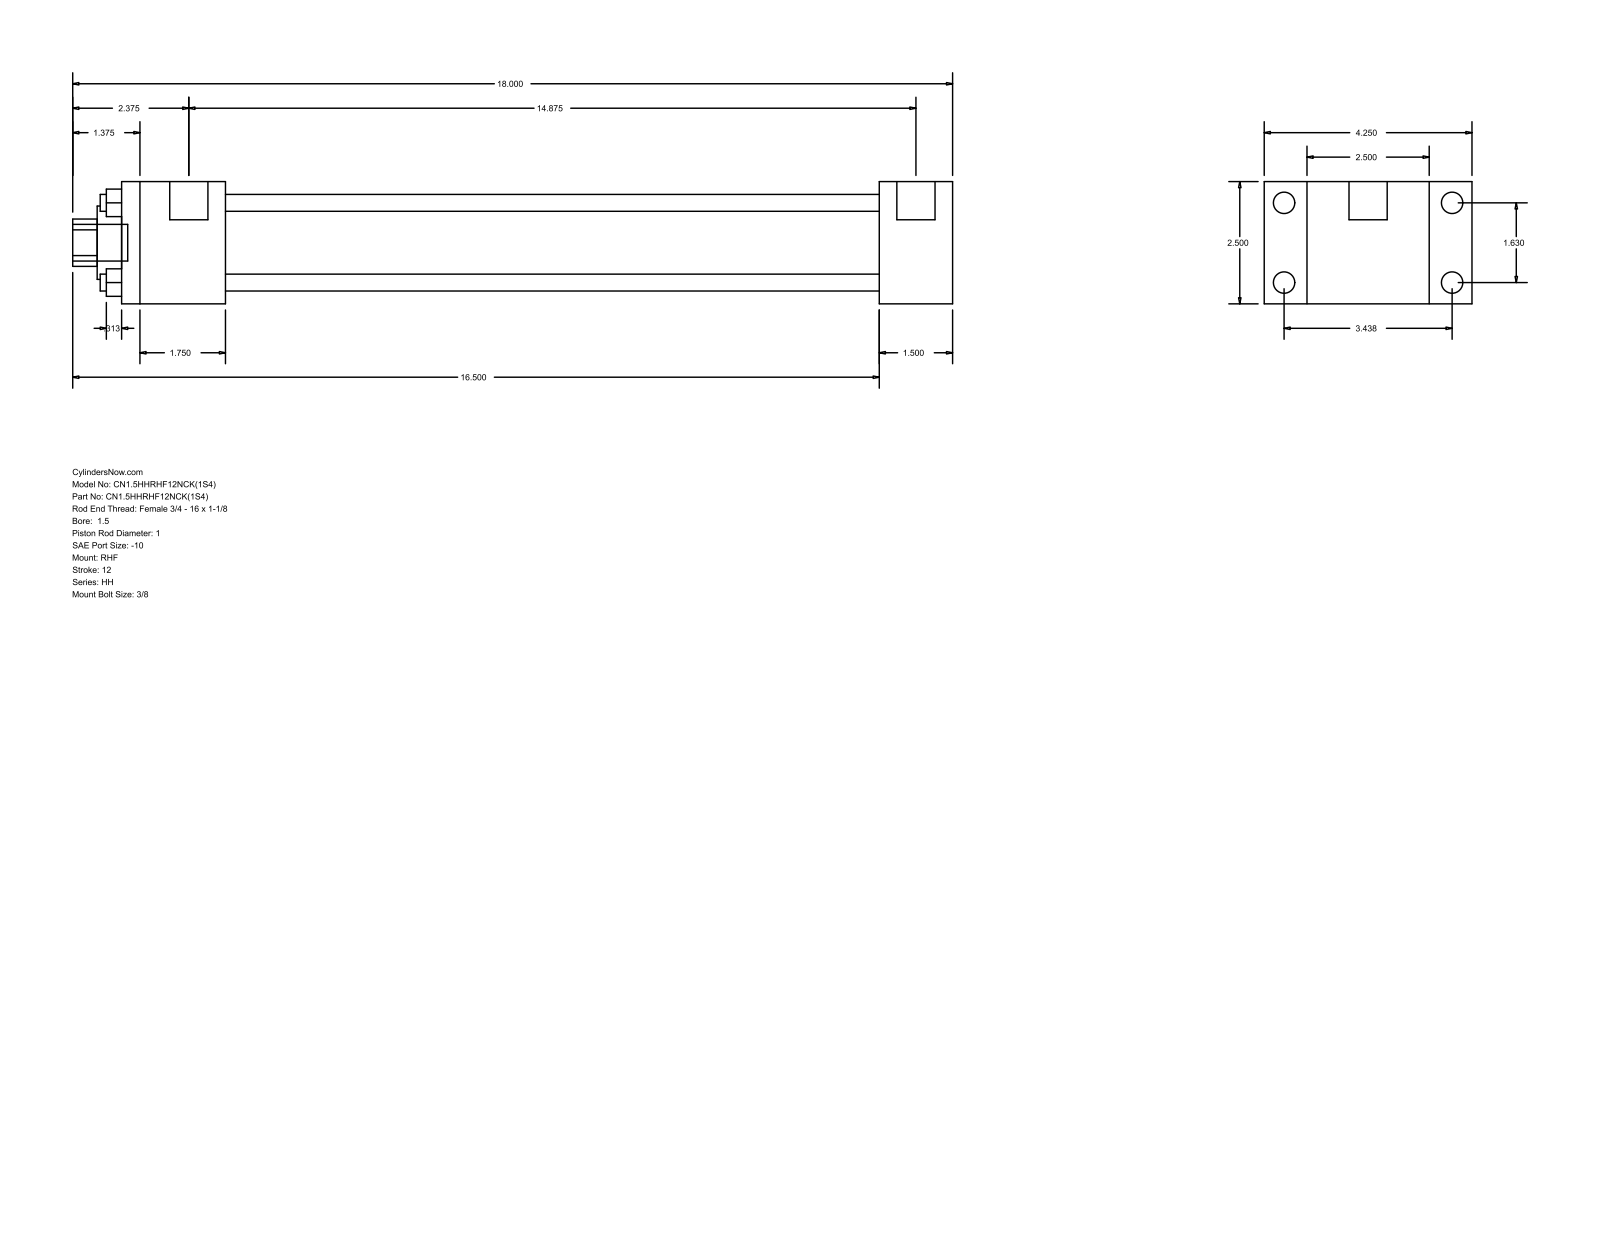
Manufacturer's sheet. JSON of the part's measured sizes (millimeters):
{"part_name": "HH_RHF__0150_1", "step_written_by": "GSSL Pune (CONFIG_CONTROL_DESIGN)", "units": "millimeters", "bodies": {"solids": 0, "faces": 88, "planar": 60, "cylindrical": 28, "other": 0}, "overall_size": [457.2, 107.95, 63.5], "round_holes": [[8.76, 4], [25.4, 1], [38.1, 1], [44.45, 1]], "round_bosses_or_shafts": [[11.13, 4], [5.56, 4], [19.84, 2], [19.05, 1]], "partial_cylinders_radius": [[12.29, 1]], "face_to_face_distances": [63.5, 22.23, 85.73, 38.1, 107.96, 339.72, 377.82, 53.98, 393.7, 431.8], "hole_center_spacings": [29.27, 41.4, 58.55]}
